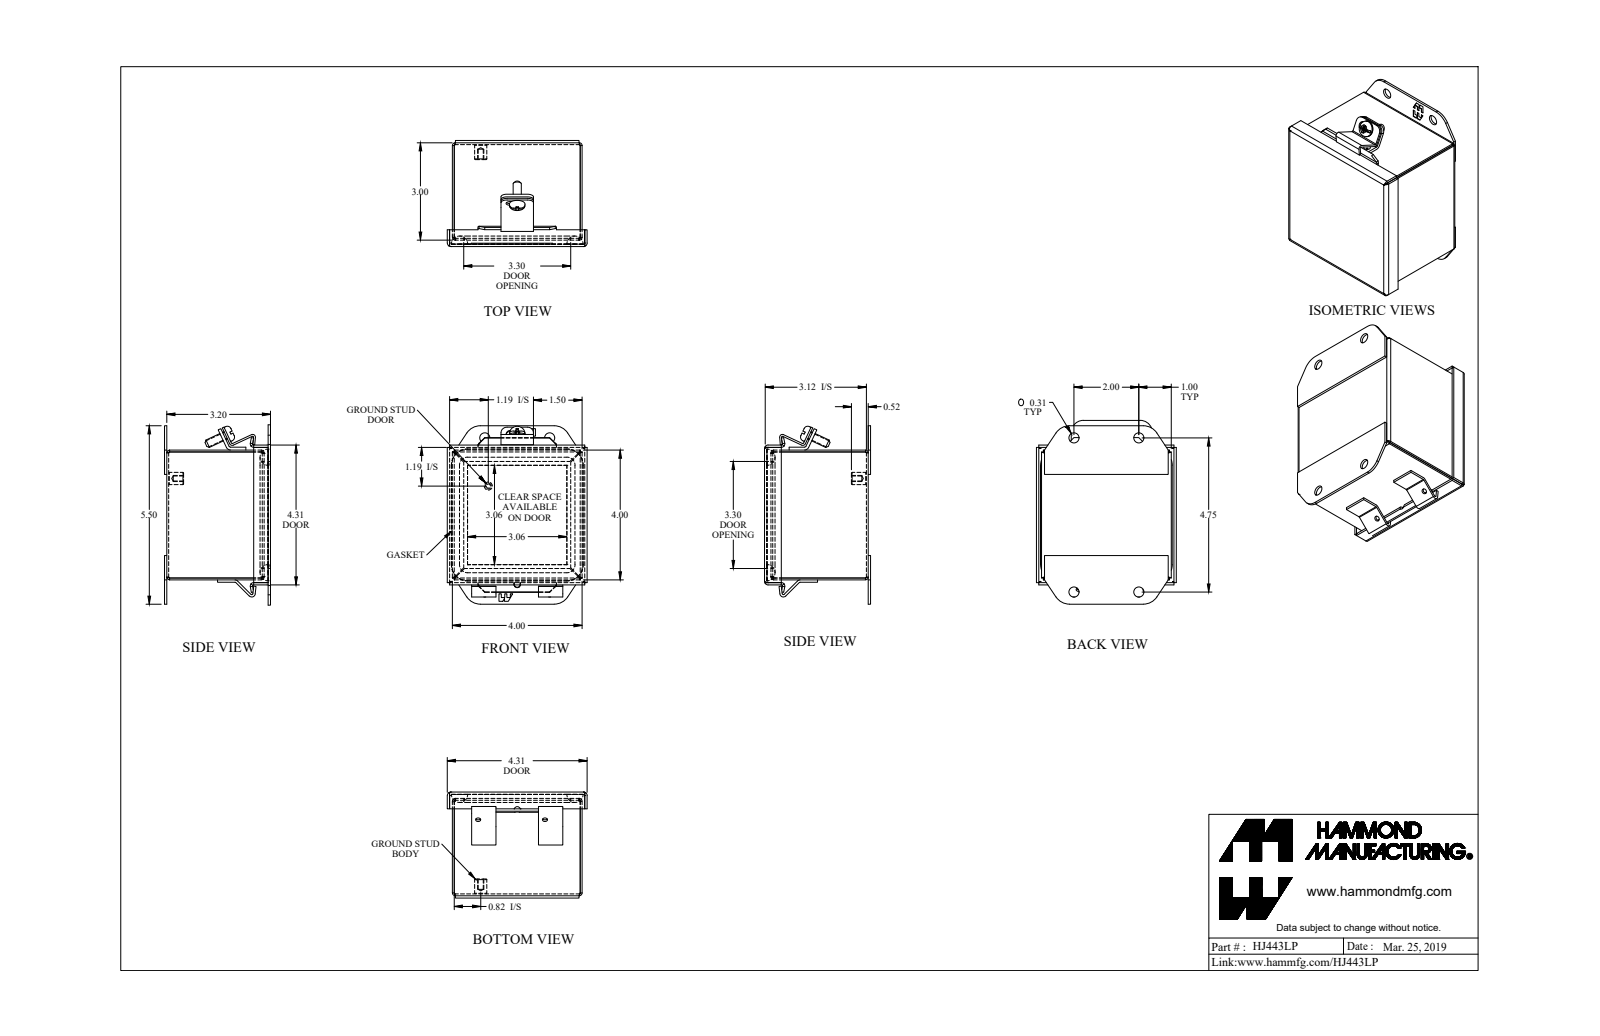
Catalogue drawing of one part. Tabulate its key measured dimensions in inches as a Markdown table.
| quantity | value |
| --- | --- |
| part name | HJ443LP |
| STEP written by | SolidWorks 2018 (AUTOMOTIVE_DESIGN) |
| units | inches |
| bodies | 12 solids, 470 faces (274 planar, 120 cylindrical, 76 other) |
| overall size | 5.5 × 4.312 × 3.269 |
| volume | 8.197 in³ |
| surface area | 255.6 in² |
| round holes (diameter × count) | 0.313 × 4, 0.156 × 2, 0.156 × 1, 0.213 × 1 |
| round bosses / shafts (diameter × count) | 0.25 × 2, 0.48 × 1, 0.375 × 1, 0.188 × 1 |
| partial cylindrical surfaces (radius × count) | 0.188 × 14, 0.029 × 10, 0.086 × 10, 0.036 × 8, 0.108 × 8, 0.25 × 4, 0.499 × 4, 0.5 × 4 |
| main face-to-face distances | 0.057, 3.943, 0.072, 3.197, 3.125, 4, 3.886, 0.057, 3.068, 3.14 |
| hole center spacings | 2, 4.75, 5.154, 1.257, 2.06, 2.466, 3.502, 4.094 |
